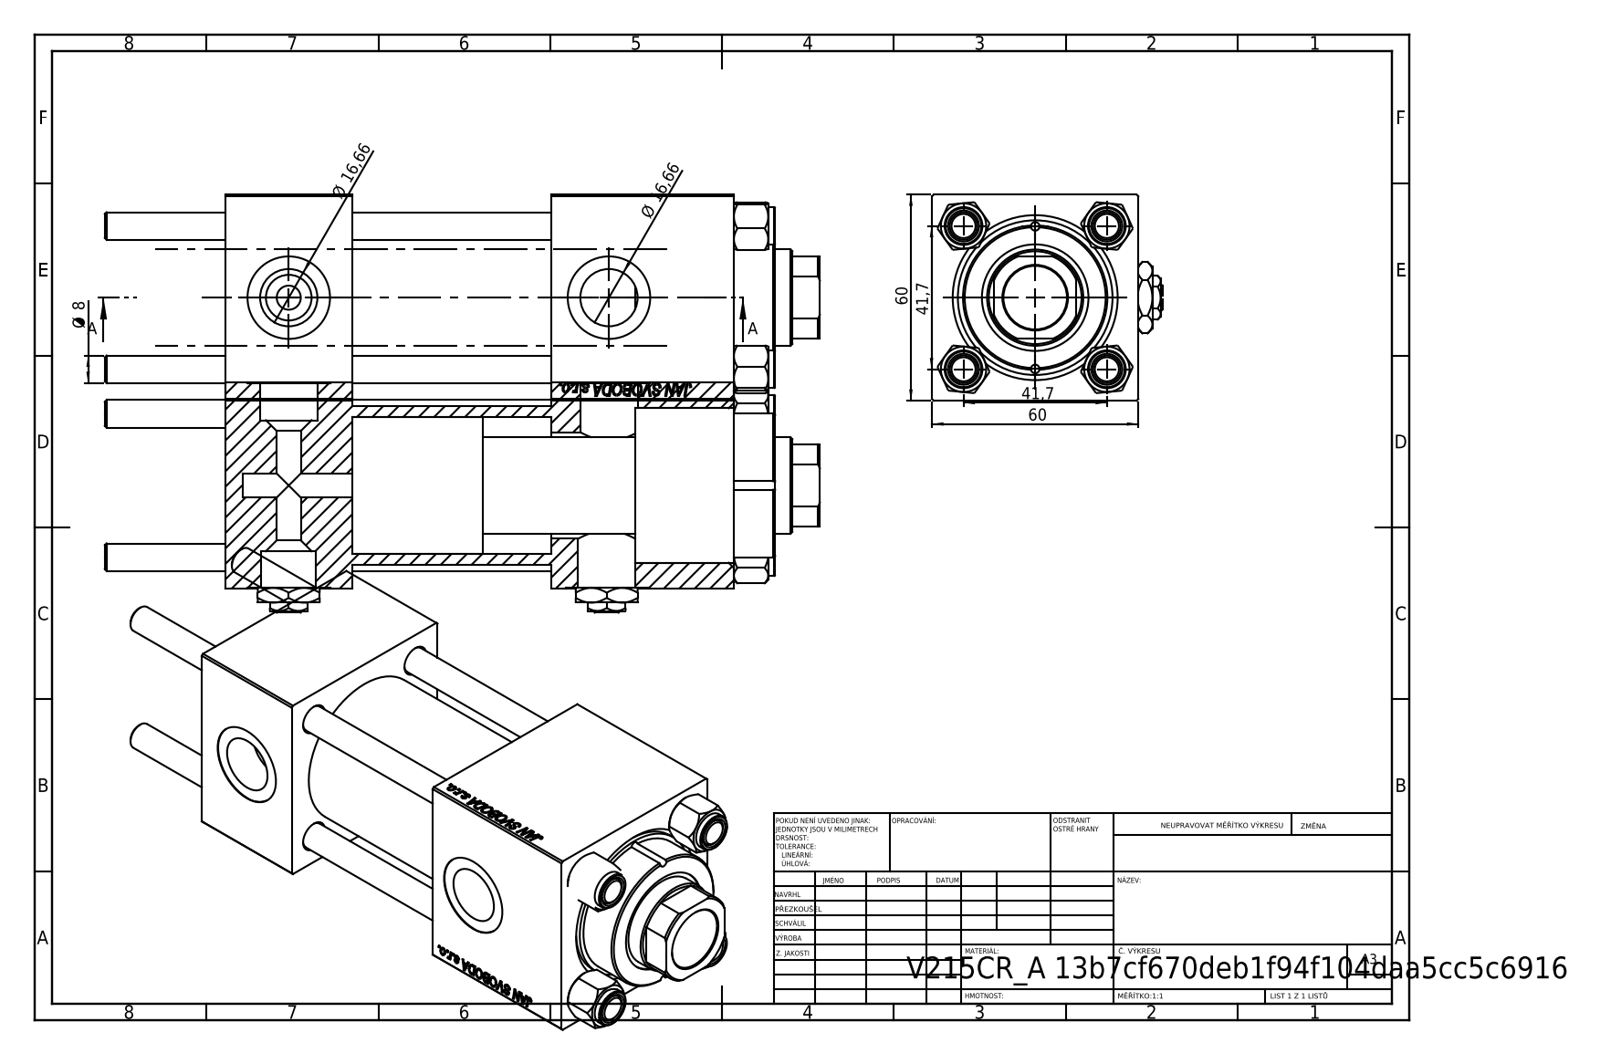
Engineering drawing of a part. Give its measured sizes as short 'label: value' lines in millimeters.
name: NUT_M5; V215CR_VCP; V215CR_BODY_A; Zatka_pro_OIL_PORT (+2 more)
written by: SolidWorks 2019 (CONFIG_CONTROL_DESIGN)
unit: mm
bodies: 13 solids, 1240 faces (568 planar, 94 cylindrical, 578 other)
size: 208 × 67 × 60
volume: 431 595 mm³; area: 123 212 mm²
holes: 4× ⌀8, 3× ⌀16.66, 3× ⌀24, 2× ⌀2.5, 2× ⌀7, 1× ⌀16, 1× ⌀18.5, 1× ⌀28, 1× ⌀31, 1× ⌀40, 1× ⌀45
bosses: 4× ⌀11, 1× ⌀46, 1× ⌀42
rounds: 1× R13.5
face distances: 60, 37, 58, 95, 53, 148, 111, 119.3, 82.3, 24.3
hole spacings: 20.85, 29.49, 41.7, 46.53, 20.75, 58.97, 0.66, 41.5
